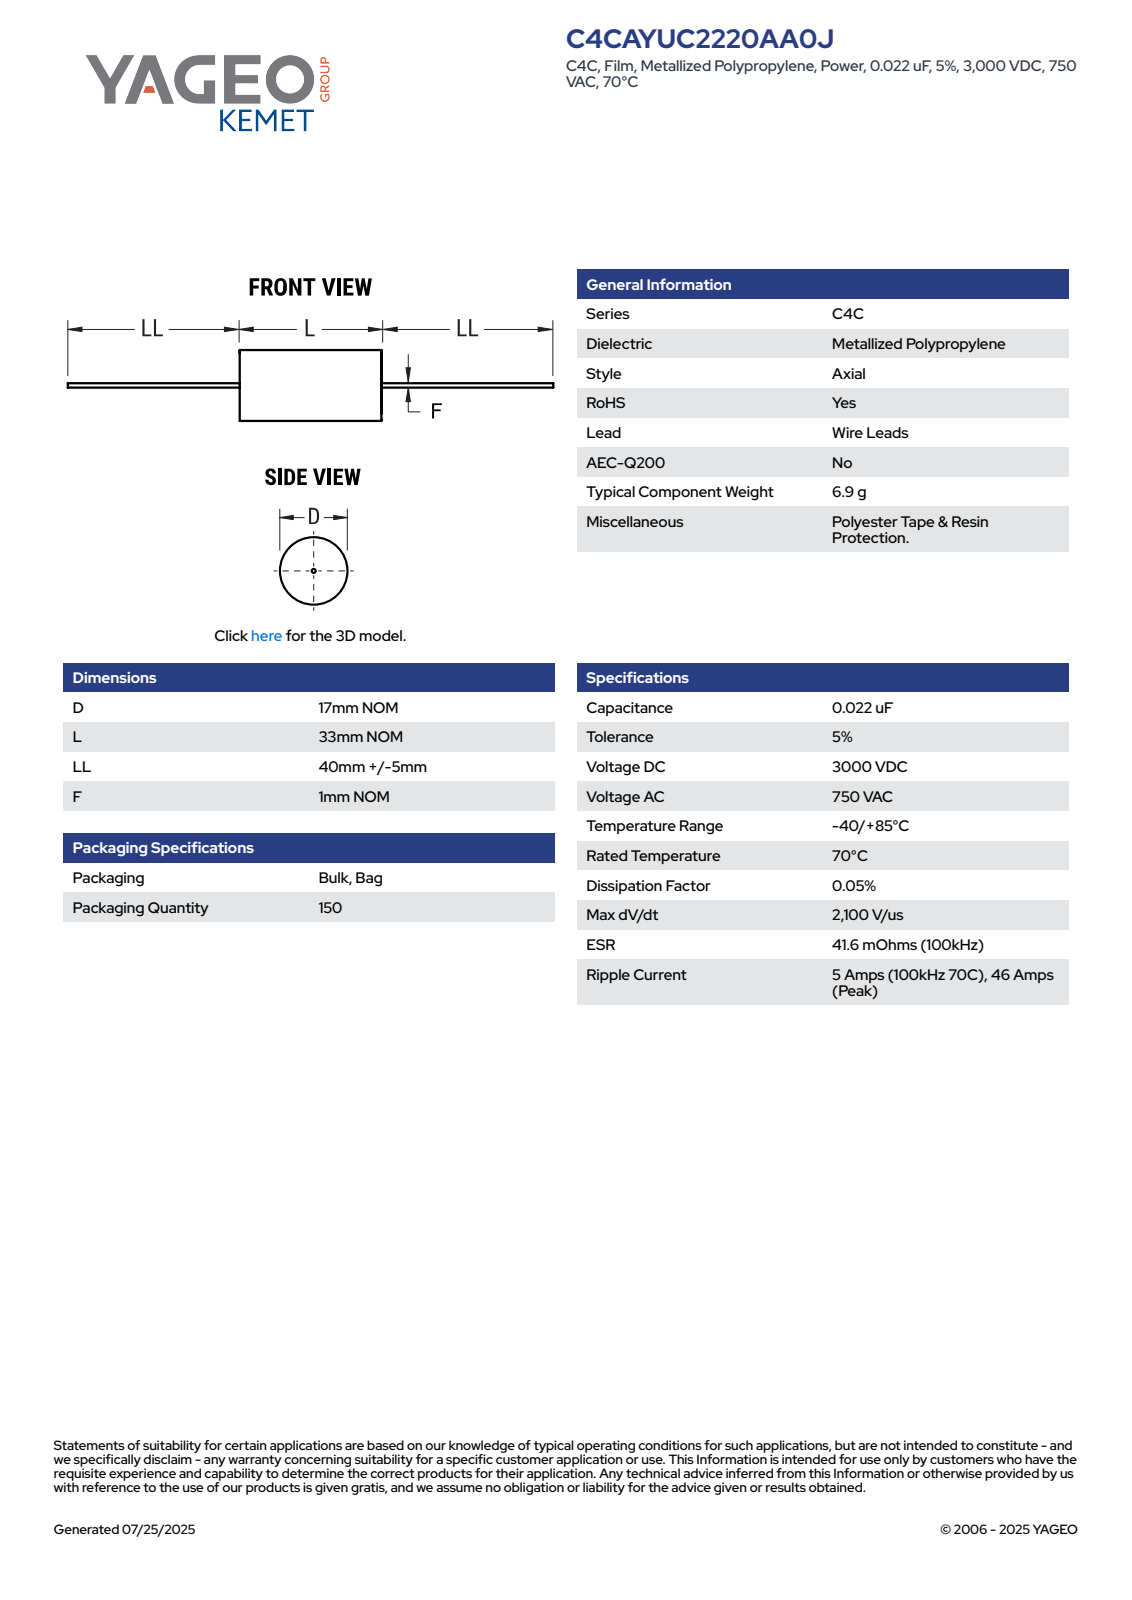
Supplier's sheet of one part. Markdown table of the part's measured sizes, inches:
| quantity | value |
| --- | --- |
| part name | CFP_ACWF_17X33_D17L33LL45F1 |
| STEP written by | SolidWorks 2014 (AUTOMOTIVE_DESIGN) |
| units | inches |
| bodies | 2 solids, 87 faces (28 planar, 28 cylindrical, 31 other) |
| overall size | 4.843 × 0.669 × 0.669 |
| volume | 0.461 in³ |
| surface area | 4.576 in² |
| round bosses / shafts (diameter × count) | 0.669 × 1, 0.039 × 1 |
| partial cylindrical surfaces (radius × count) | 0.334 × 1 |
| main face-to-face distances | 1.3, 1.299, 1.772, 3.071, 1.771, 4.843, 3.071 |
